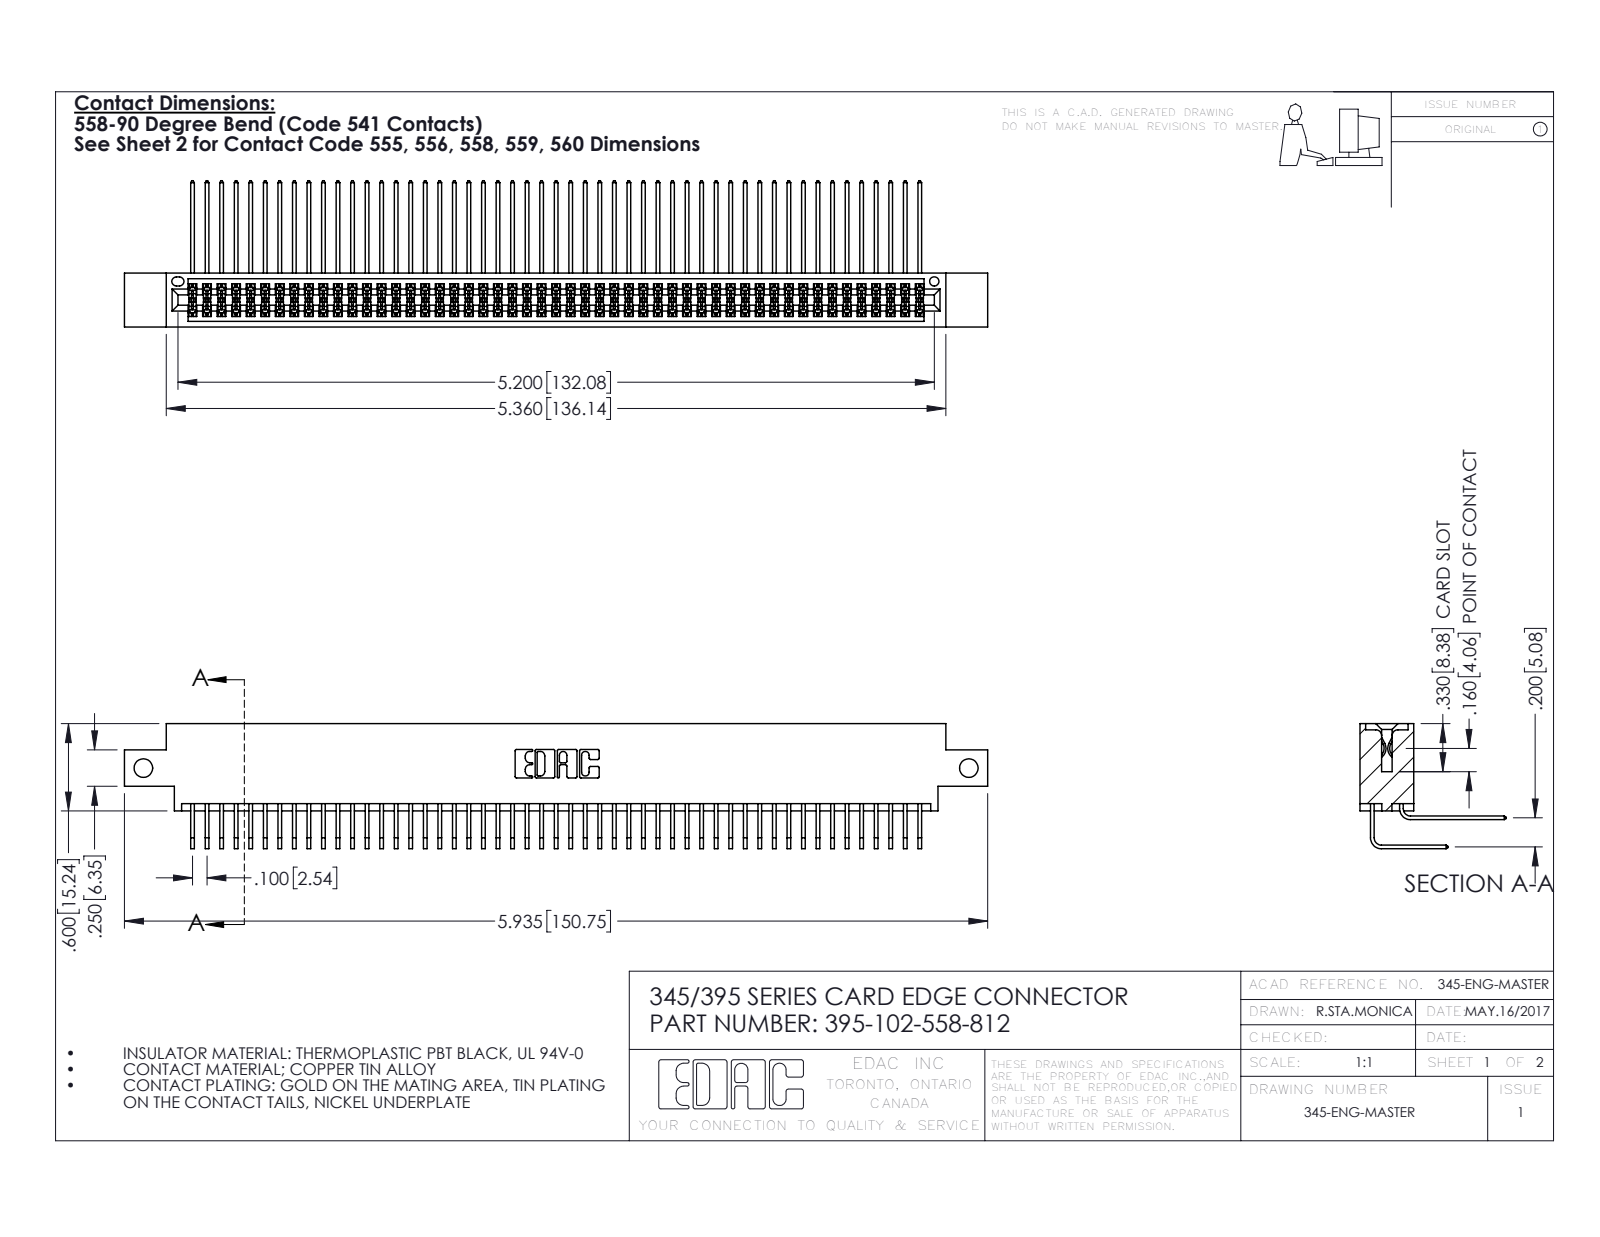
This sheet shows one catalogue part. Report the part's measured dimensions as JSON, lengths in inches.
{"part_name": "395-102-558-812; 345-292-001_558 559 Tail - 1; 345 Part_0.170 Offset - Side Mount; 345-292-001_558 Tail - 2", "step_written_by": "SolidWorks 2016 (CONFIG_CONTROL_DESIGN)", "units": "inches", "bodies": {"solids": 103, "faces": 5434, "planar": 3654, "cylindrical": 1780, "other": 0}, "overall_size": [5.935, 1.005, 0.859], "volume_in3": 0.922, "surface_area_in2": 39.2, "round_holes": [[0.128, 2], [0.064, 1]], "partial_cylinders_radius": [[0.006, 154], [0.01, 22], [0.007, 6], [0.031, 6], [0.026, 3], [0.014, 2], [0.019, 2], [0.022, 2]], "face_to_face_distances": [0.072, 0.298, 0.2, 0.37, 0.098, 0.272, 0.025, 0.225, 0.175, 0.025], "hole_center_spacings": [5.675]}
